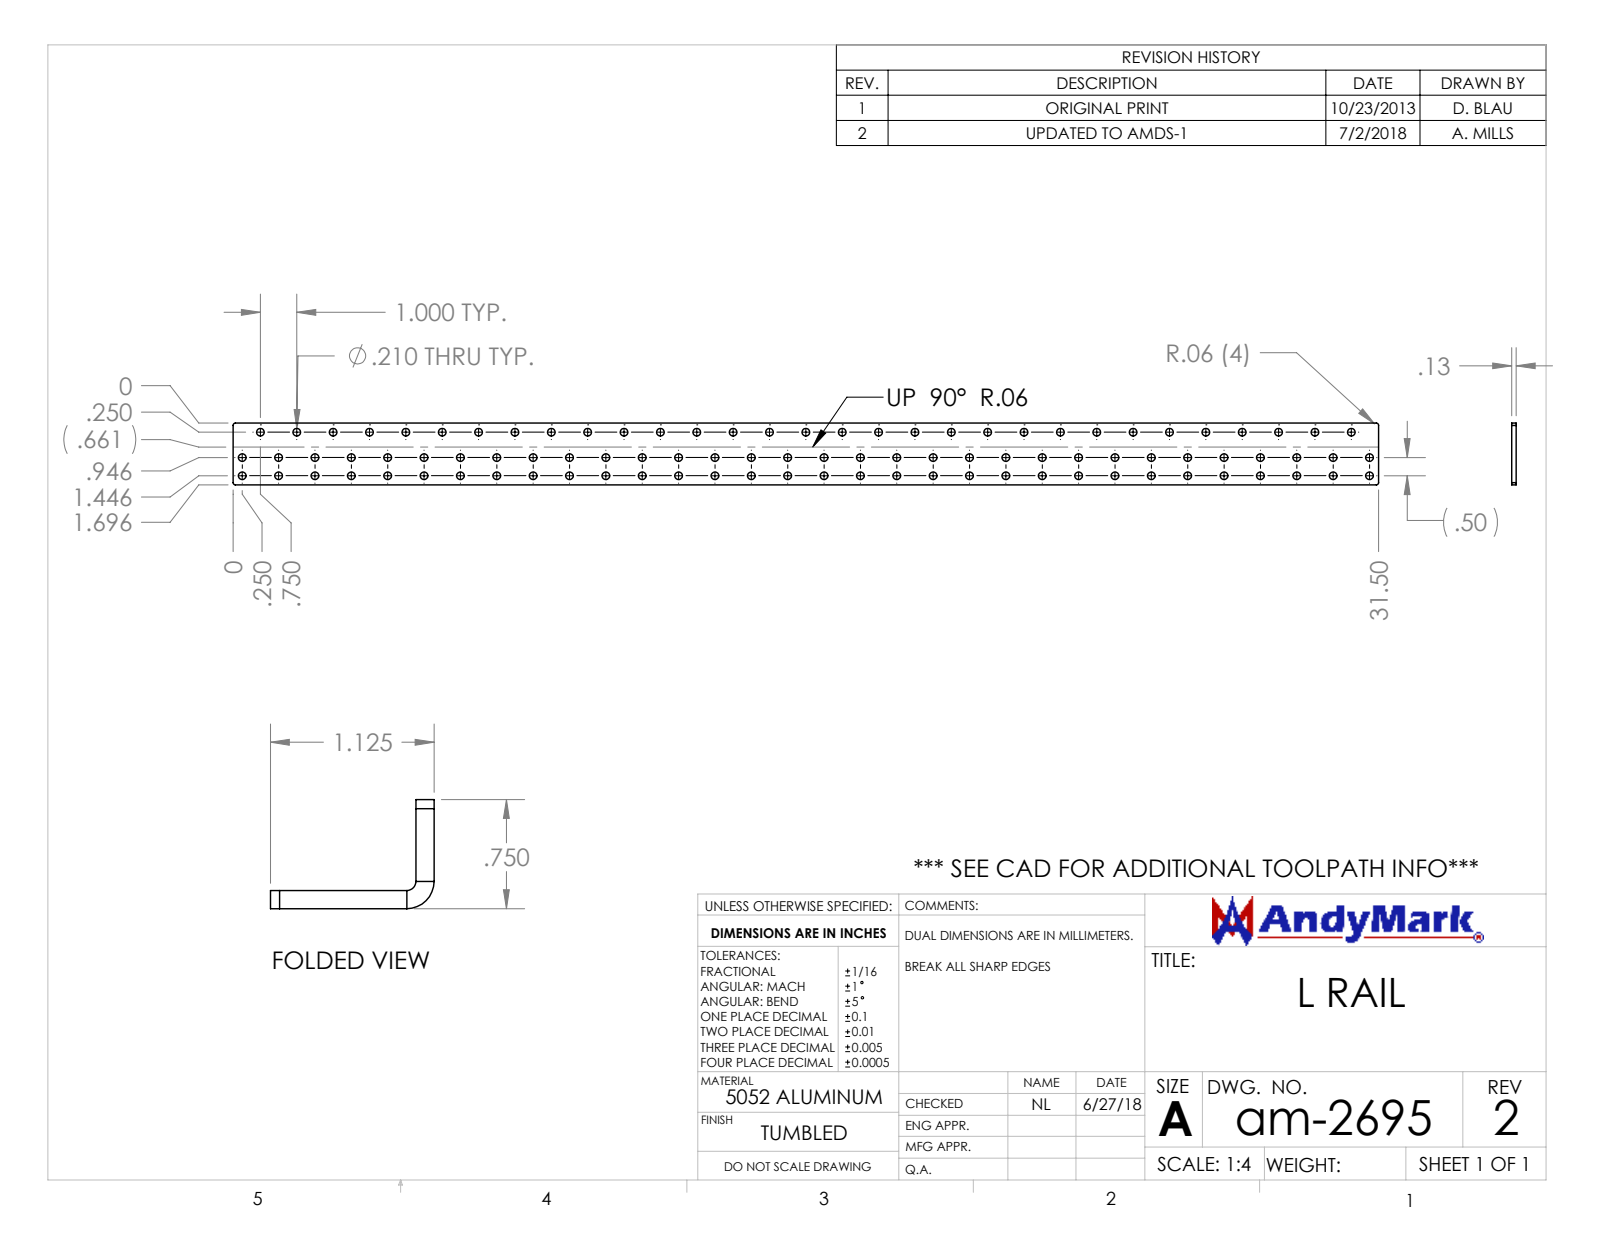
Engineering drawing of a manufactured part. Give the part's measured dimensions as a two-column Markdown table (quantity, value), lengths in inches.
| quantity | value |
| --- | --- |
| part name | am-2695 L-Rail REV2 |
| STEP written by | SolidWorks 2017 (AUTOMOTIVE_DESIGN) |
| units | inches |
| bodies | 1 solid, 200 faces (6 planar, 194 cylindrical, 0 other) |
| overall size | 31.5 × 1.696 × 0.125 |
| volume | 6.268 in³ |
| surface area | 116.4 in² |
| round holes (diameter × count) | 0.21 × 95 |
| partial cylindrical surfaces (radius × count) | 0.062 × 4 |
| main face-to-face distances | 0.125, 1.696, 31.5 |
| hole center spacings | 1, 1.118, 2, 2.061, 3, 3.041, 4, 4.031 |
